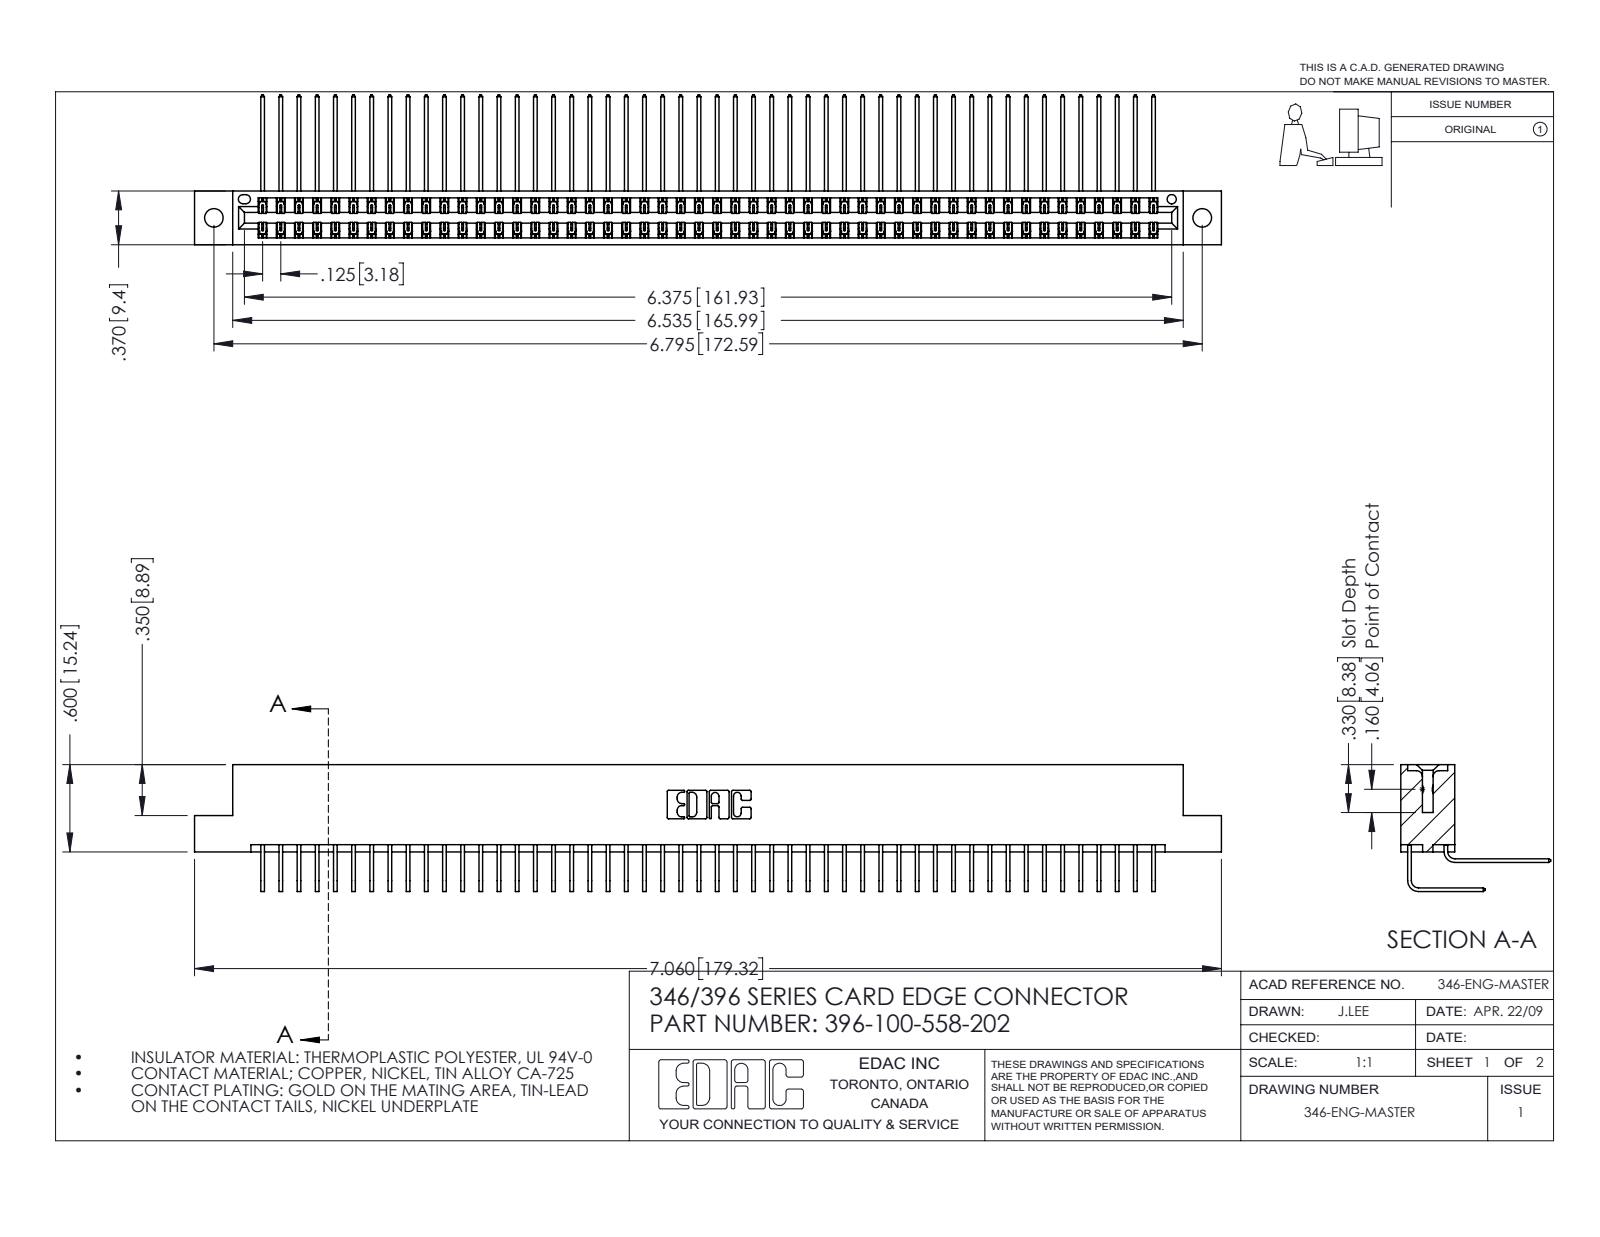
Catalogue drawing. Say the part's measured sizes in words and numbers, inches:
The part is named "396-100-558-202; 345-292-001_558 Tail - 2; 346 Part_Flush Mounting Lugs - 0.128 Dia; 345-292-001_558 559 Tail - 1". Its 3-D file was written by "SolidWorks 2016 (CONFIG_CONTROL_DESIGN)". It is 101 solids with 5522 faces: 3776 planar, 1746 cylindrical and 0 other. Overall it measures 7.06 by 1.03 by 0.873 inches. Its volume is 1.104 cubic inches and its surface area 42.61 square inches. Round holes: 2 of diameter 0.128, 1 of diameter 0.064. Partial cylindrical surfaces (rounded edges, fillets, slot ends): 150 of radius 0.006, 22 of radius 0.01, 6 of radius 0.007, 6 of radius 0.031, 3 of radius 0.026, 2 of radius 0.014, 2 of radius 0.022, 2 of radius 0.024. The main face-to-face distances are 0.322, 0.048, 0.025, 0.37, 0.25, 0.298, 0.072, 0.275, 0.148, 0.222. The hole center spacings are 0.246, 6.586, 6.795.
